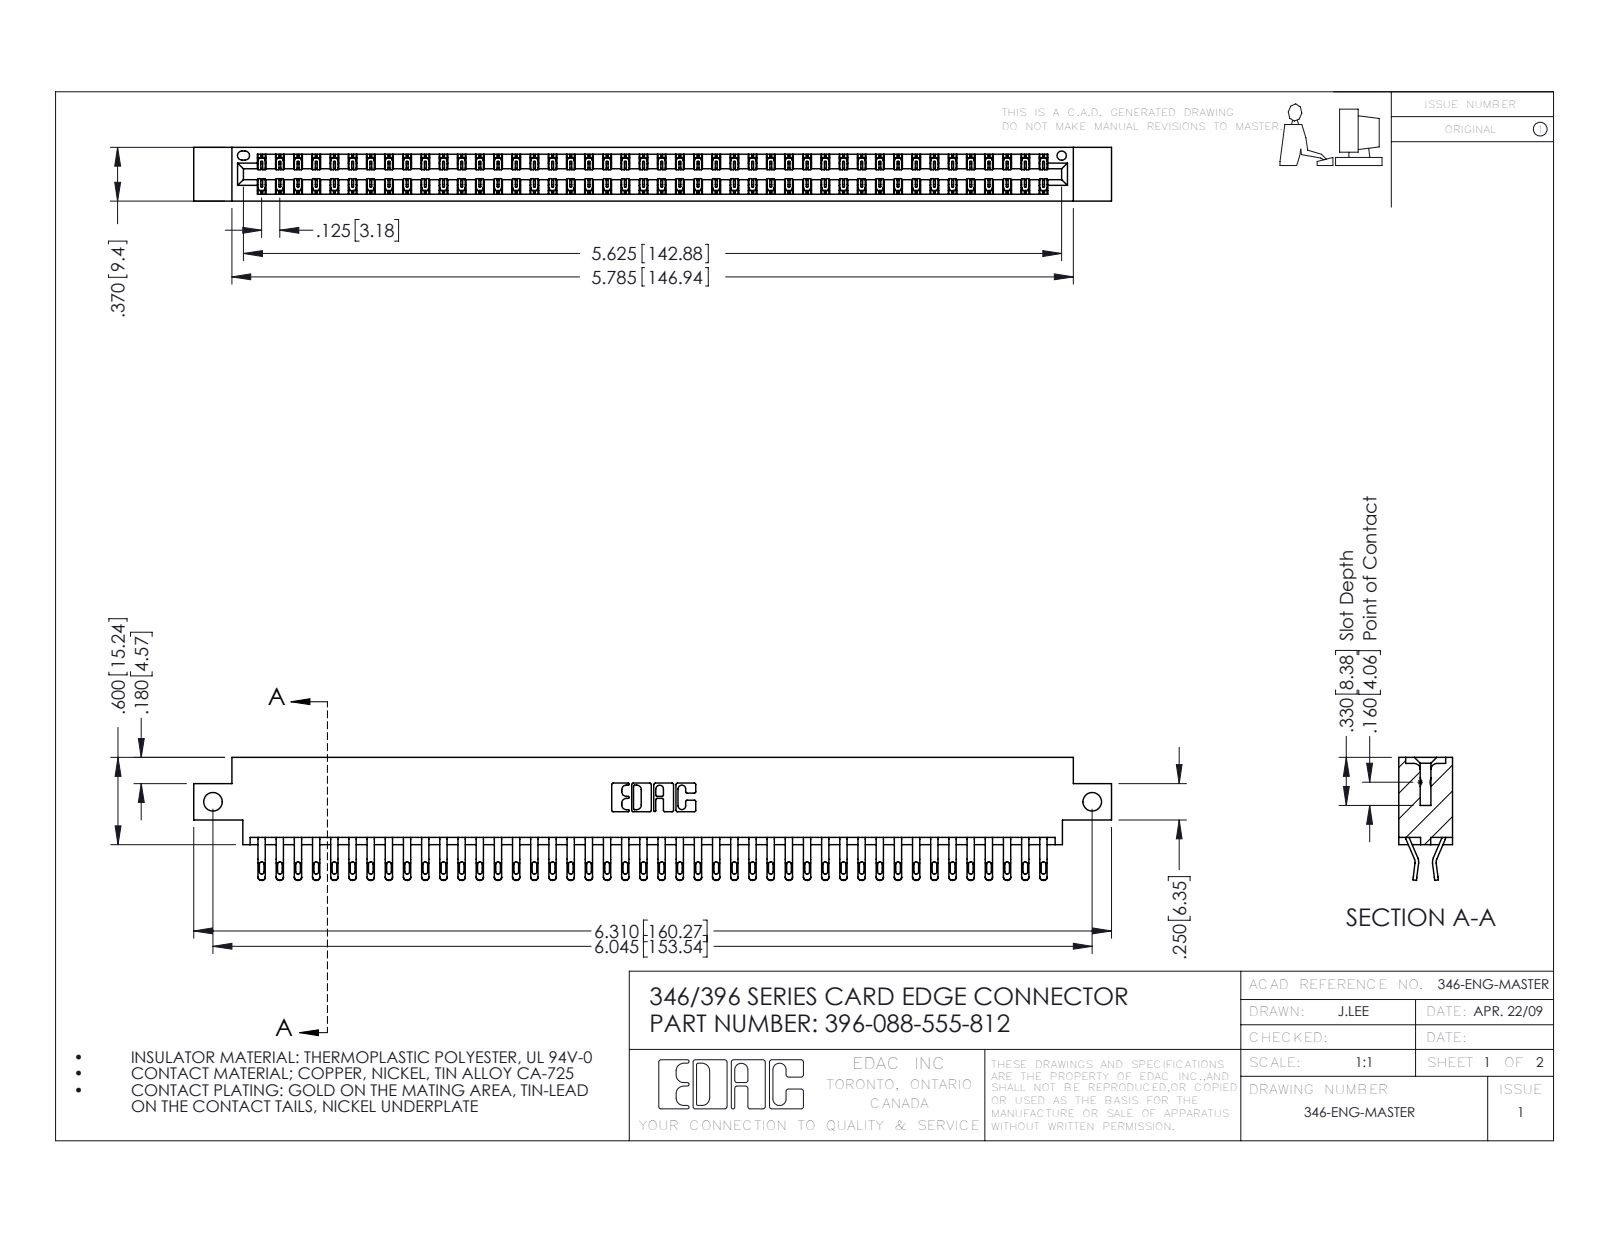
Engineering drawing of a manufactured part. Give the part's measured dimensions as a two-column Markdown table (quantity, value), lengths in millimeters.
| quantity | value |
| --- | --- |
| part name | 345-292-001_555 Tail; 396-088-555-812; 346 Part_0.170 Offset - Side Mount |
| STEP written by | SolidWorks 2016 (CONFIG_CONTROL_DESIGN) |
| units | millimeters |
| bodies | 89 solids, 5230 faces (2984 planar, 2246 cylindrical, 0 other) |
| overall size | 160.3 × 21.5 × 9.4 |
| volume | 15 600 mm³ |
| surface area | 22 500 mm² |
| round holes (diameter × count) | 3.3 × 2, 1.6 × 1 |
| partial cylindrical surfaces (radius × count) | 0.4 × 176, 0.5 × 176, 0.2 × 132, 0.3 × 22, 0.2 × 6, 0.8 × 6, 0.7 × 3, 0.3 × 2 |
| main face-to-face distances | 1.2, 8.2, 9.4, 6.4, 0.6, 1.8, 7.6, 7, 3.8, 5.6 |
| hole center spacings | 153.5 |
